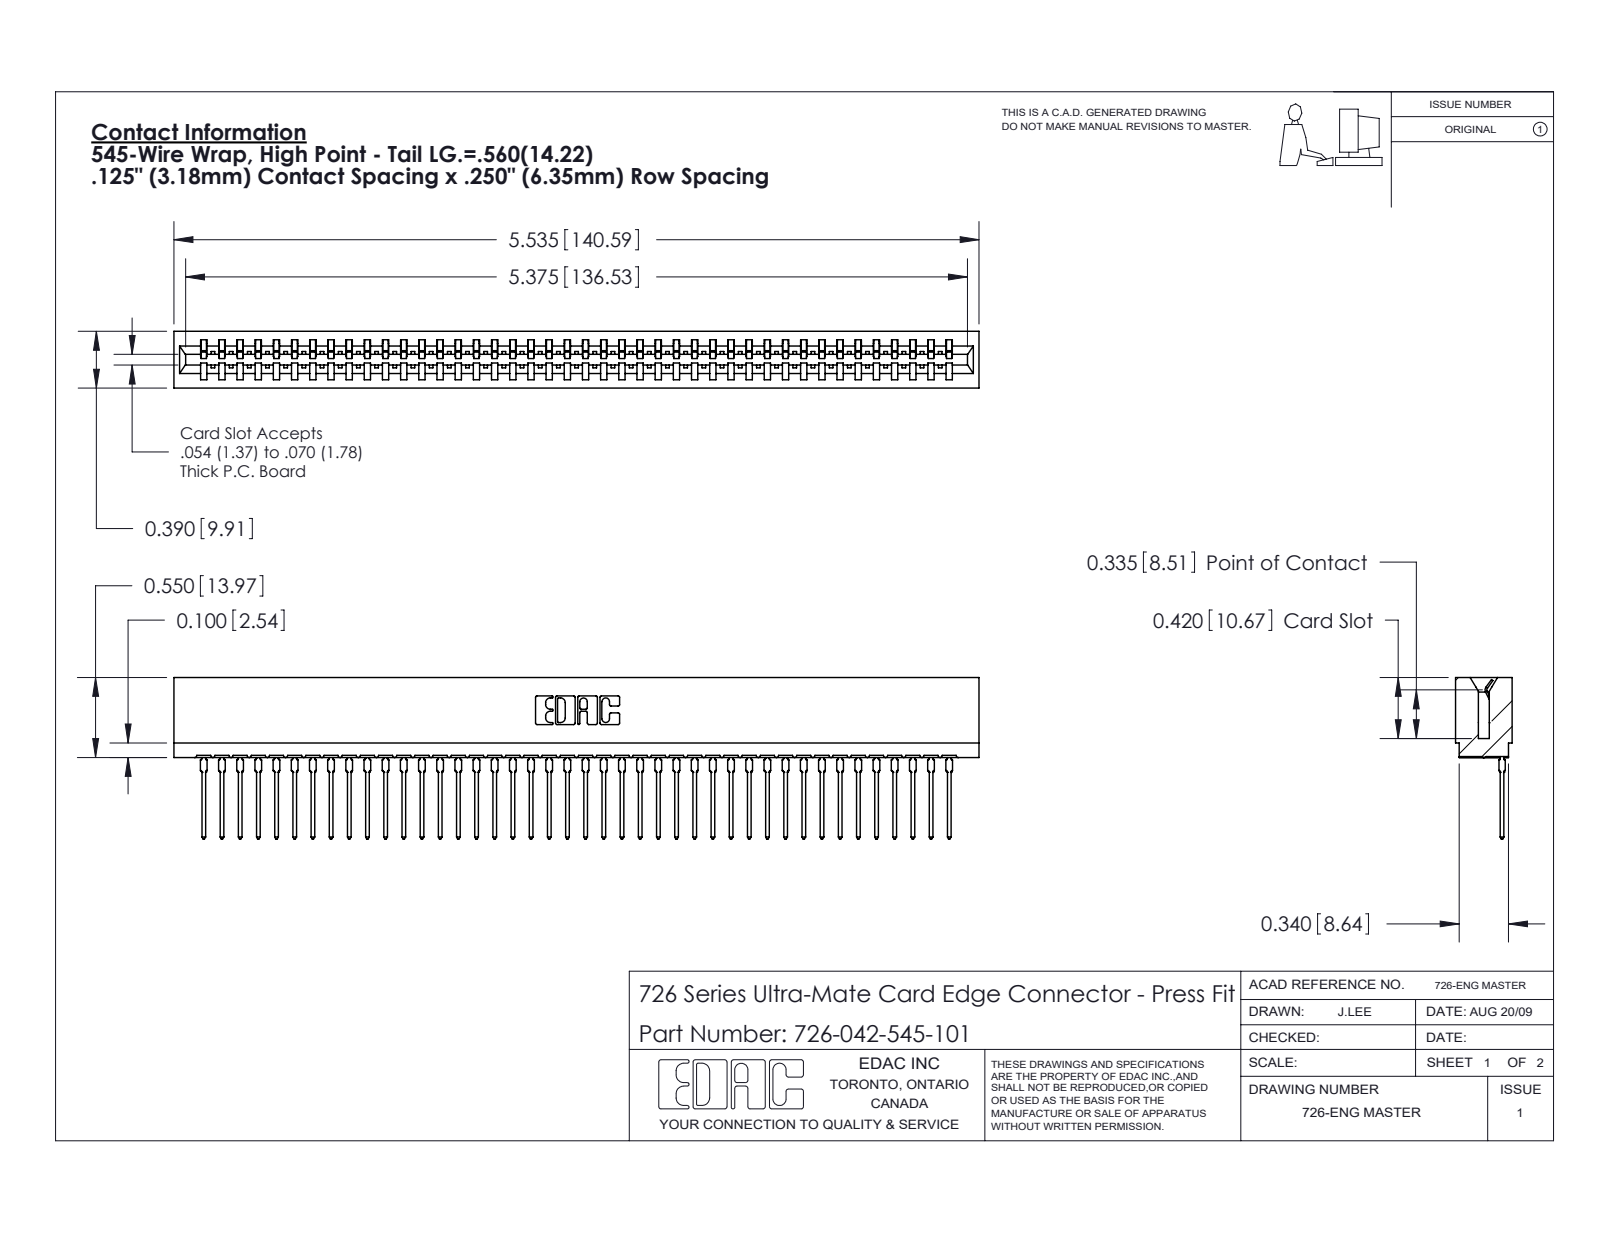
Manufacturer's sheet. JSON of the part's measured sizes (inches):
{"part_name": "726-042-545-101; 746-292-001_545; 726 Part_.515 Slot Depth - 01", "step_written_by": "SolidWorks 2020 (CONFIG_CONTROL_DESIGN)", "units": "inches", "bodies": {"solids": 43, "faces": 4633, "planar": 2701, "cylindrical": 840, "other": 1092}, "overall_size": [5.535, 1.109, 0.39], "volume_in3": 0.773, "surface_area_in2": 30.88, "partial_cylinders_radius": [[0.021, 84], [0.015, 43], [0.01, 22], [0.007, 6], [0.031, 6], [0.005, 4], [0.011, 4], [0.026, 3]], "face_to_face_distances": [0.057, 0.333, 0.39, 0.025, 0.307, 0.25, 0.083, 0.275, 0.5, 0.365]}
